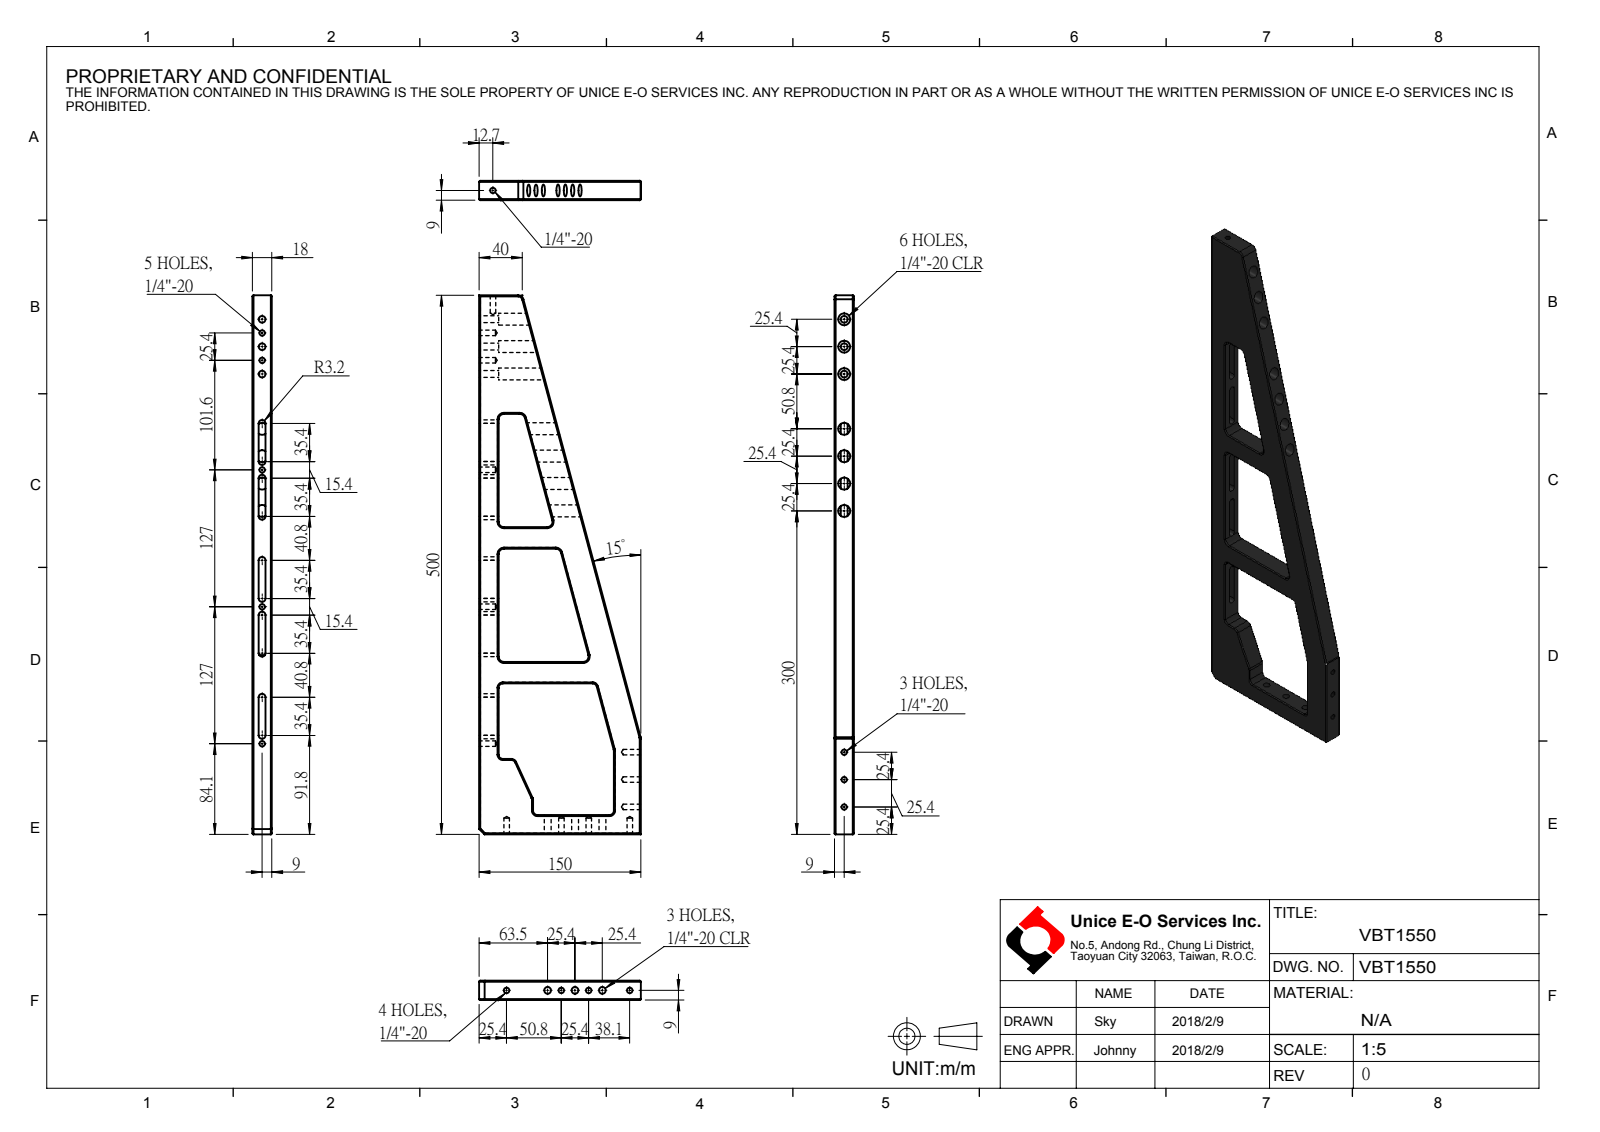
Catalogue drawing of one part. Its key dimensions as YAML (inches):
part_name: "U-F1-VBT1550E1-D0; VBT1550"
step_written_by: "SolidWorks 2016 (AUTOMOTIVE_DESIGN)"
units: inches
bodies: {solids: 1, faces: 225, planar: 37, cylindrical: 126, other: 62}
overall_size: [19.685, 5.906, 0.709]
volume: 29.62
surface_area: 179.3
round_holes:
  - {diameter: 0.201, count: 13}
  - {diameter: 0.25, count: 6}
  - {diameter: 0.437, count: 4}
  - {diameter: 0.433, count: 3}
partial_cylinders:
  - {radius: 0.039, count: 38}
  - {radius: 0.197, count: 12}
  - {radius: 0.126, count: 10}
  - {radius: 0.157, count: 6}
face_to_face_distances: [0.709, 0.228, 0.48, 0.252, 4.921, 0.787, 1.07, 5.197, 5.906, 5.512]
hole_center_spacings: [1, 0.5, 2, 1.5, 5, 3, 3.5, 4]
